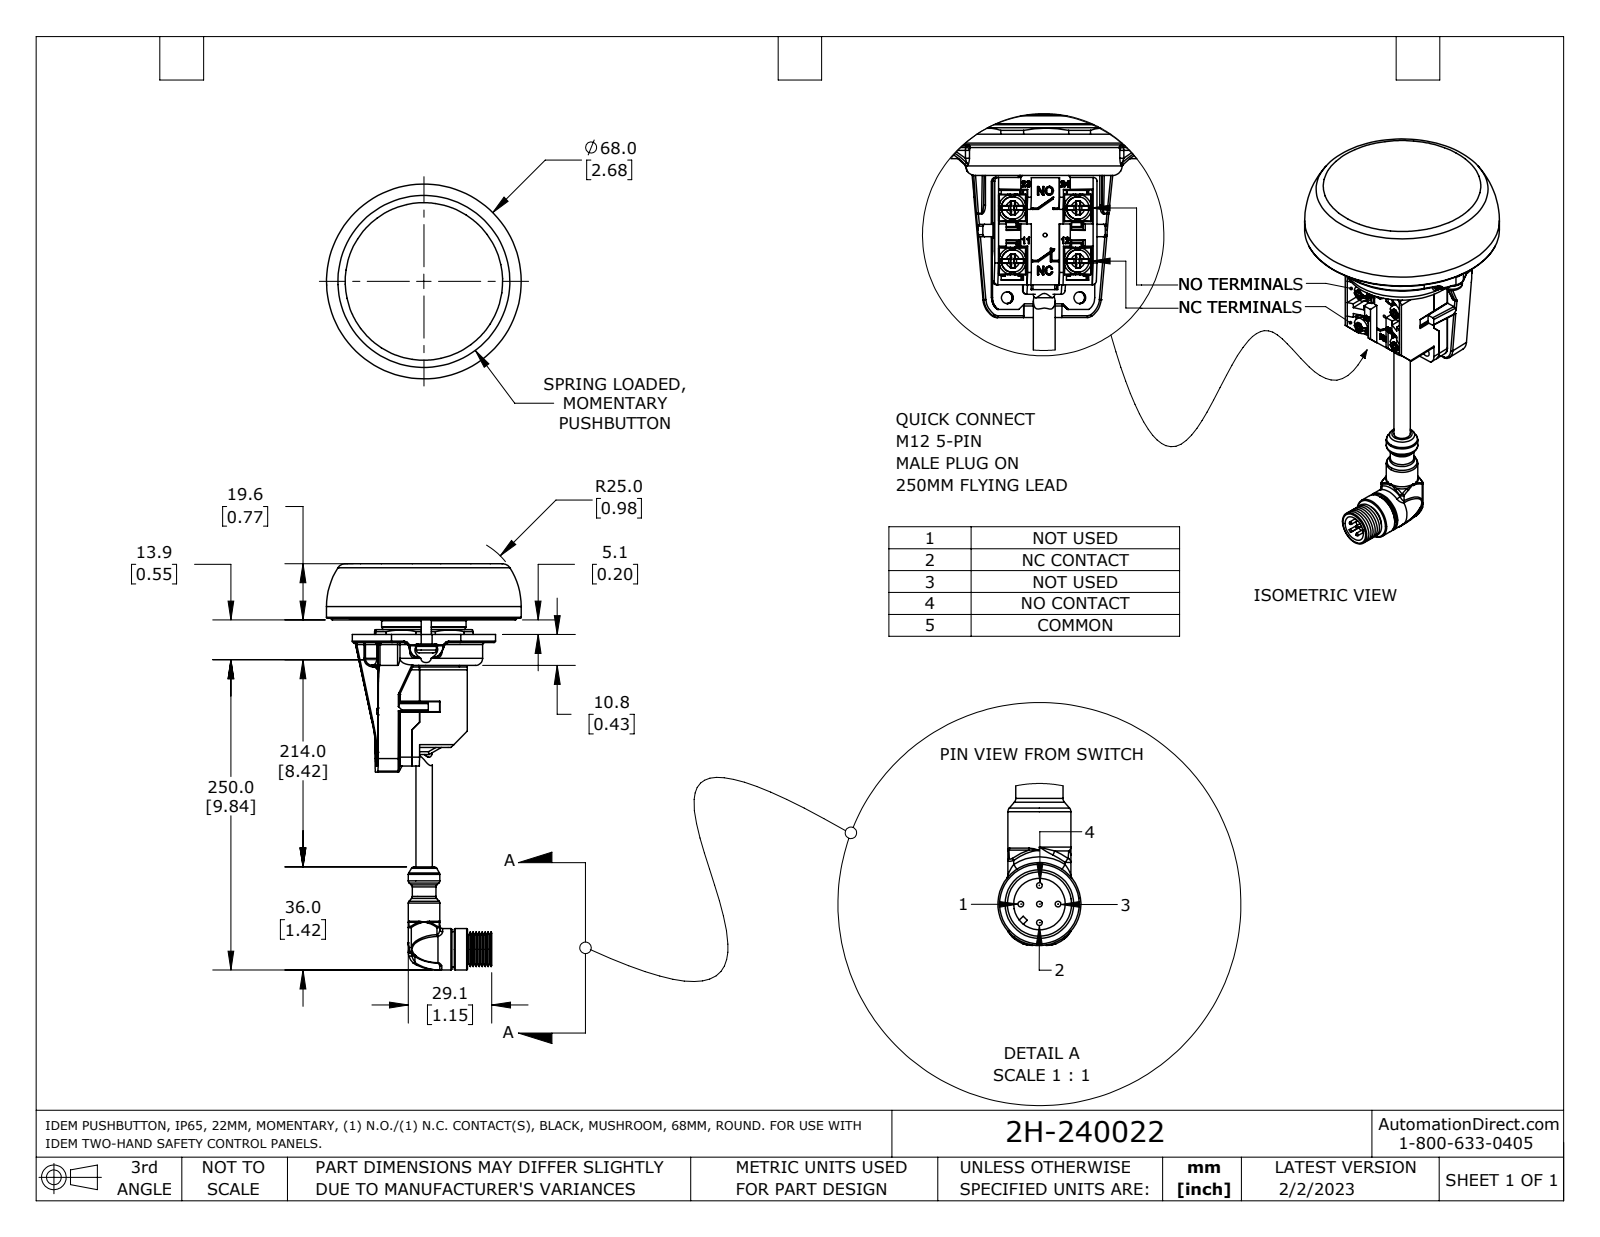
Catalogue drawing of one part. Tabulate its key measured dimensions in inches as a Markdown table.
| quantity | value |
| --- | --- |
| part name | 2H-240022 |
| STEP written by | SolidWorks 2021 (AUTOMOTIVE_DESIGN) |
| units | inches |
| bodies | 12 solids, 3040 faces (1147 planar, 823 cylindrical, 1070 other) |
| overall size | 5.583 × 2.677 × 2.677 |
| volume | 3.597 in³ |
| surface area | 85.92 in² |
| round holes (diameter × count) | 0.157 × 4, 0.083 × 2, 0.118 × 2, 0.122 × 2, 0.128 × 2, 0.138 × 2, 0.173 × 2, 0.177 × 2, 0.346 × 2, 0.224 × 1, 0.354 × 1, 0.866 × 1 |
| round bosses / shafts (diameter × count) | 0.039 × 5, 0.232 × 4, 0.135 × 4, 0.386 × 2, 0.276 × 2, 0.244 × 2, 0.138 × 2, 0.051 × 2 |
| partial cylindrical surfaces (radius × count) | 0.008 × 162, 0.012 × 149, 0.02 × 114, 0.004 × 32, 0.039 × 26, 0.016 × 16, 0.024 × 16, 0.028 × 9 |
| main face-to-face distances | 0.717, 0.055, 0.772, 0.539, 0.594, 0.177, 0.201, 0.039, 0.343, 0.079 |
| hole center spacings | 0.748, 0.945, 1.043, 1.407, 1.408, 1.89, 2.087 |
